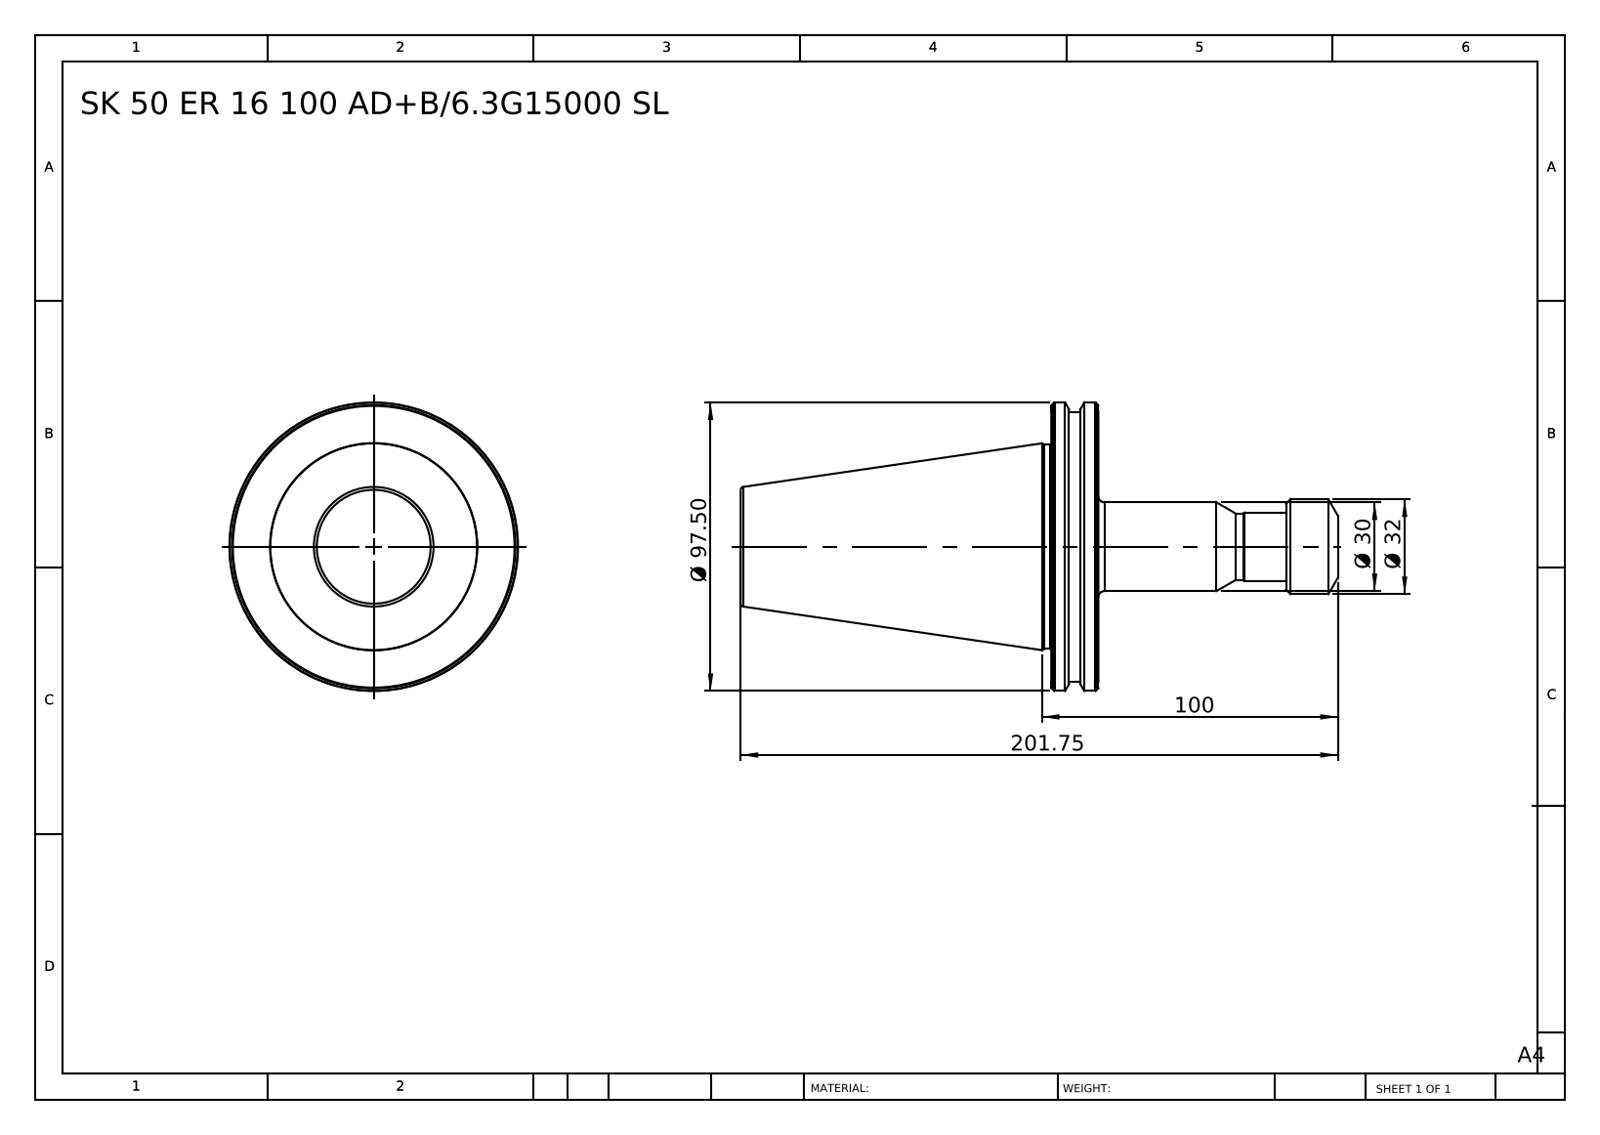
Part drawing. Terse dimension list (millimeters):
name: SK 50 ER 16 100 AD-6.3G15000 SL
written by: SolidWorks 2014 (CONFIG_CONTROL_DESIGN)
unit: mm
bodies: 1 solid, 77 faces (7 planar, 16 cylindrical, 54 other)
size: 201.75 × 97.5 × 97.5
volume: 425 548 mm³; area: 44 026 mm²
bosses: 1× ⌀97.5, 1× ⌀91, 1× ⌀69, 1× ⌀32, 1× ⌀30, 1× ⌀23, 1× ⌀22.5
face distances: 15.9, 120.85, 104.95, 80.9, 96.8, 201.75, 87, 90.8, 6.1, 9.9
